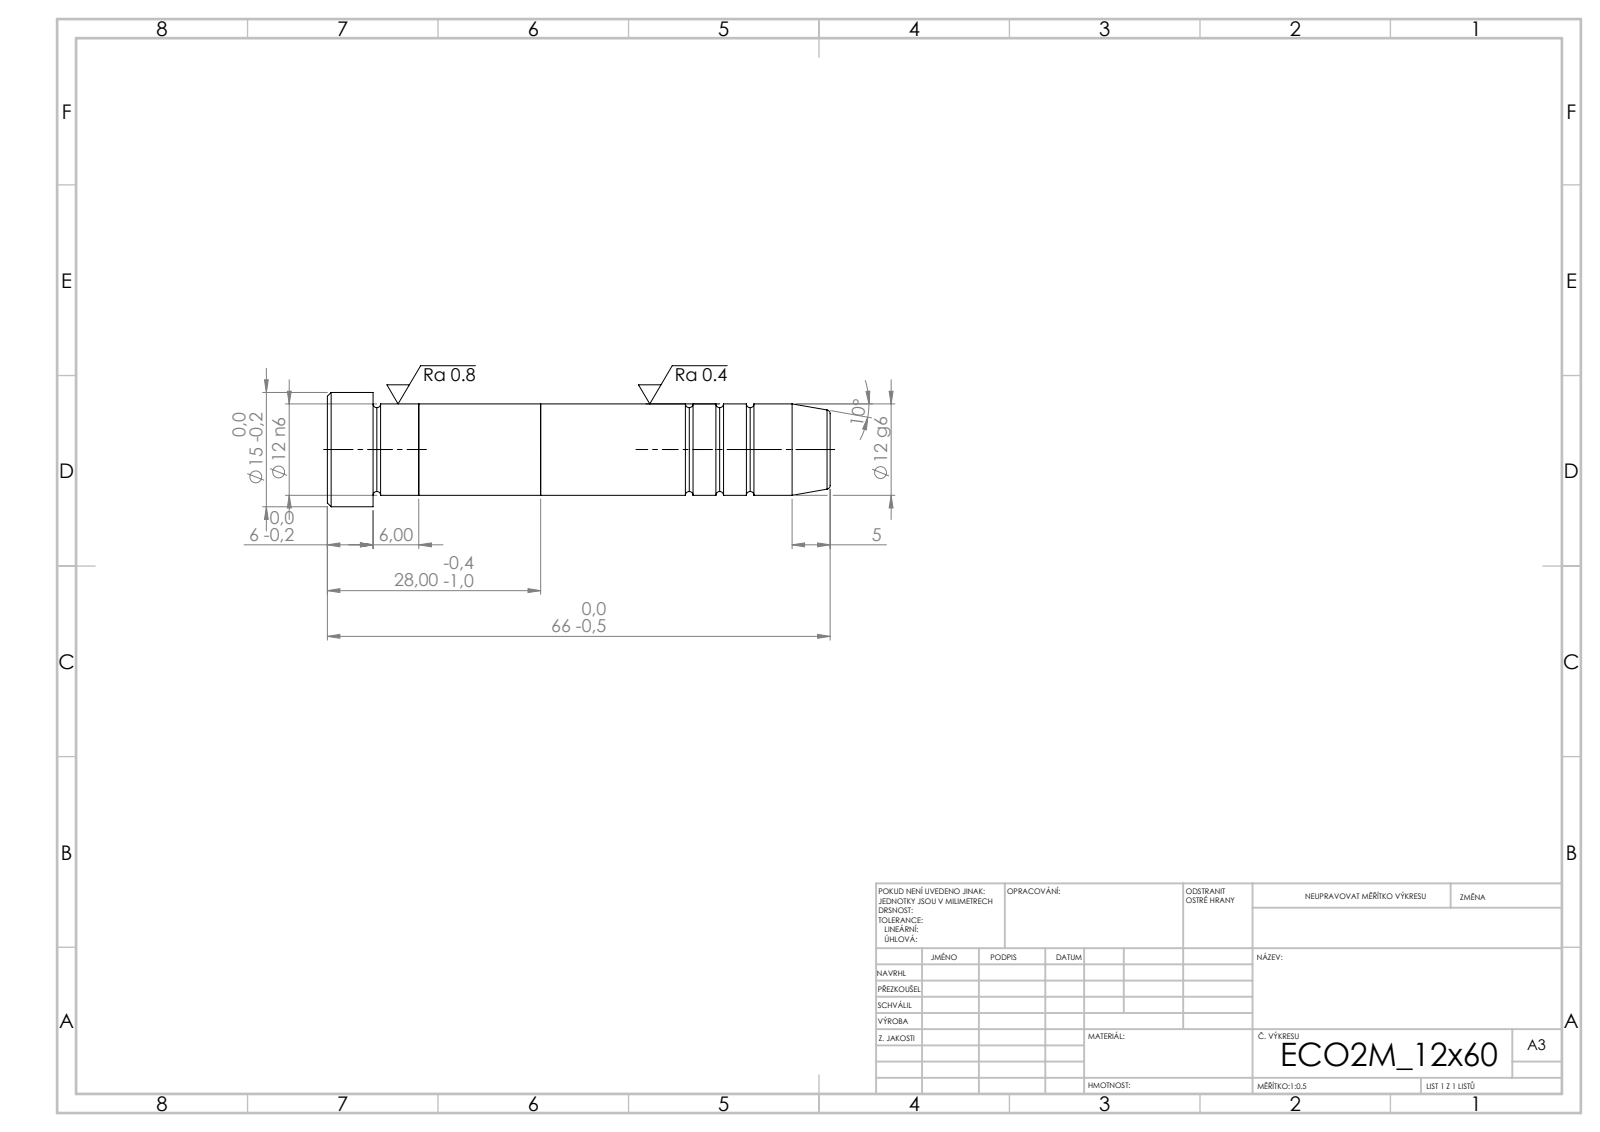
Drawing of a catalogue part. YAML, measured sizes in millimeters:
step_written_by: "SolidWorks 2019 (CONFIG_CONTROL_DESIGN)"
units: millimeters
bodies: {solids: 3, faces: 43, planar: 7, cylindrical: 14, other: 22}
overall_size: [66, 15, 15]
volume: 7703
surface_area: 3363
round_bosses_or_shafts:
  - {diameter: 15, count: 1}
  - {diameter: 12, count: 1}
face_to_face_distances: [16, 28, 12, 6, 38, 54, 66, 60, 22]
